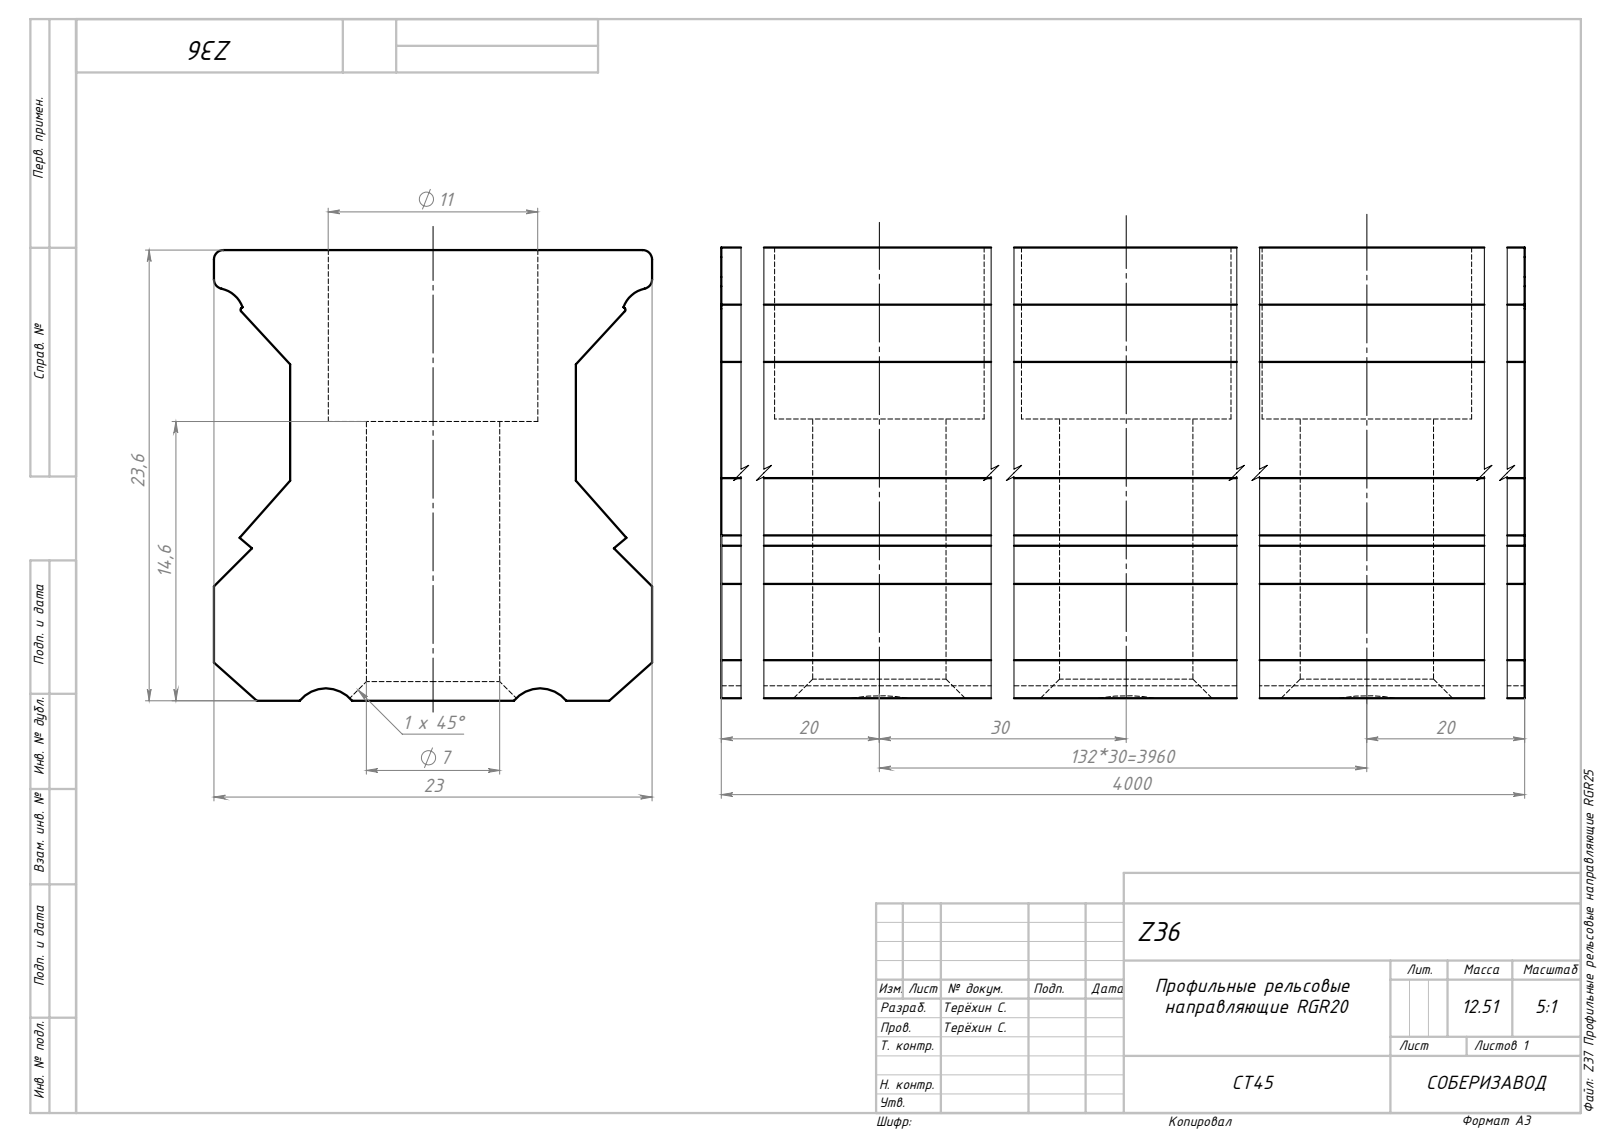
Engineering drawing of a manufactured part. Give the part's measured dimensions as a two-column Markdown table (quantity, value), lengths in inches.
| quantity | value |
| --- | --- |
| part name | Z37 Профильные рельсовые направляющие RGR25_00; Сборка2 |
| STEP written by | SolidWorks 2022 (AUTOMOTIVE_DESIGN) |
| units | inches |
| bodies | 1 solid, 1099 faces (290 planar, 543 cylindrical, 266 other) |
| overall size | 157.48 × 0.931 × 0.906 |
| volume | 97.76 in³ |
| surface area | 727.8 in² |
| round holes (diameter × count) | 0.276 × 133, 0.433 × 133 |
| partial cylindrical surfaces (radius × count) | 0.02 × 4, 0.004 × 2, 0.059 × 2, 0.07 × 2 |
| main face-to-face distances | 0.931, 0.157, 0.748, 0.591, 0.906, 0.577, 0.354, 157.48 |
| hole center spacings | 1.181, 2.362, 3.543, 4.724, 5.906, 7.087, 8.268, 9.449 |
